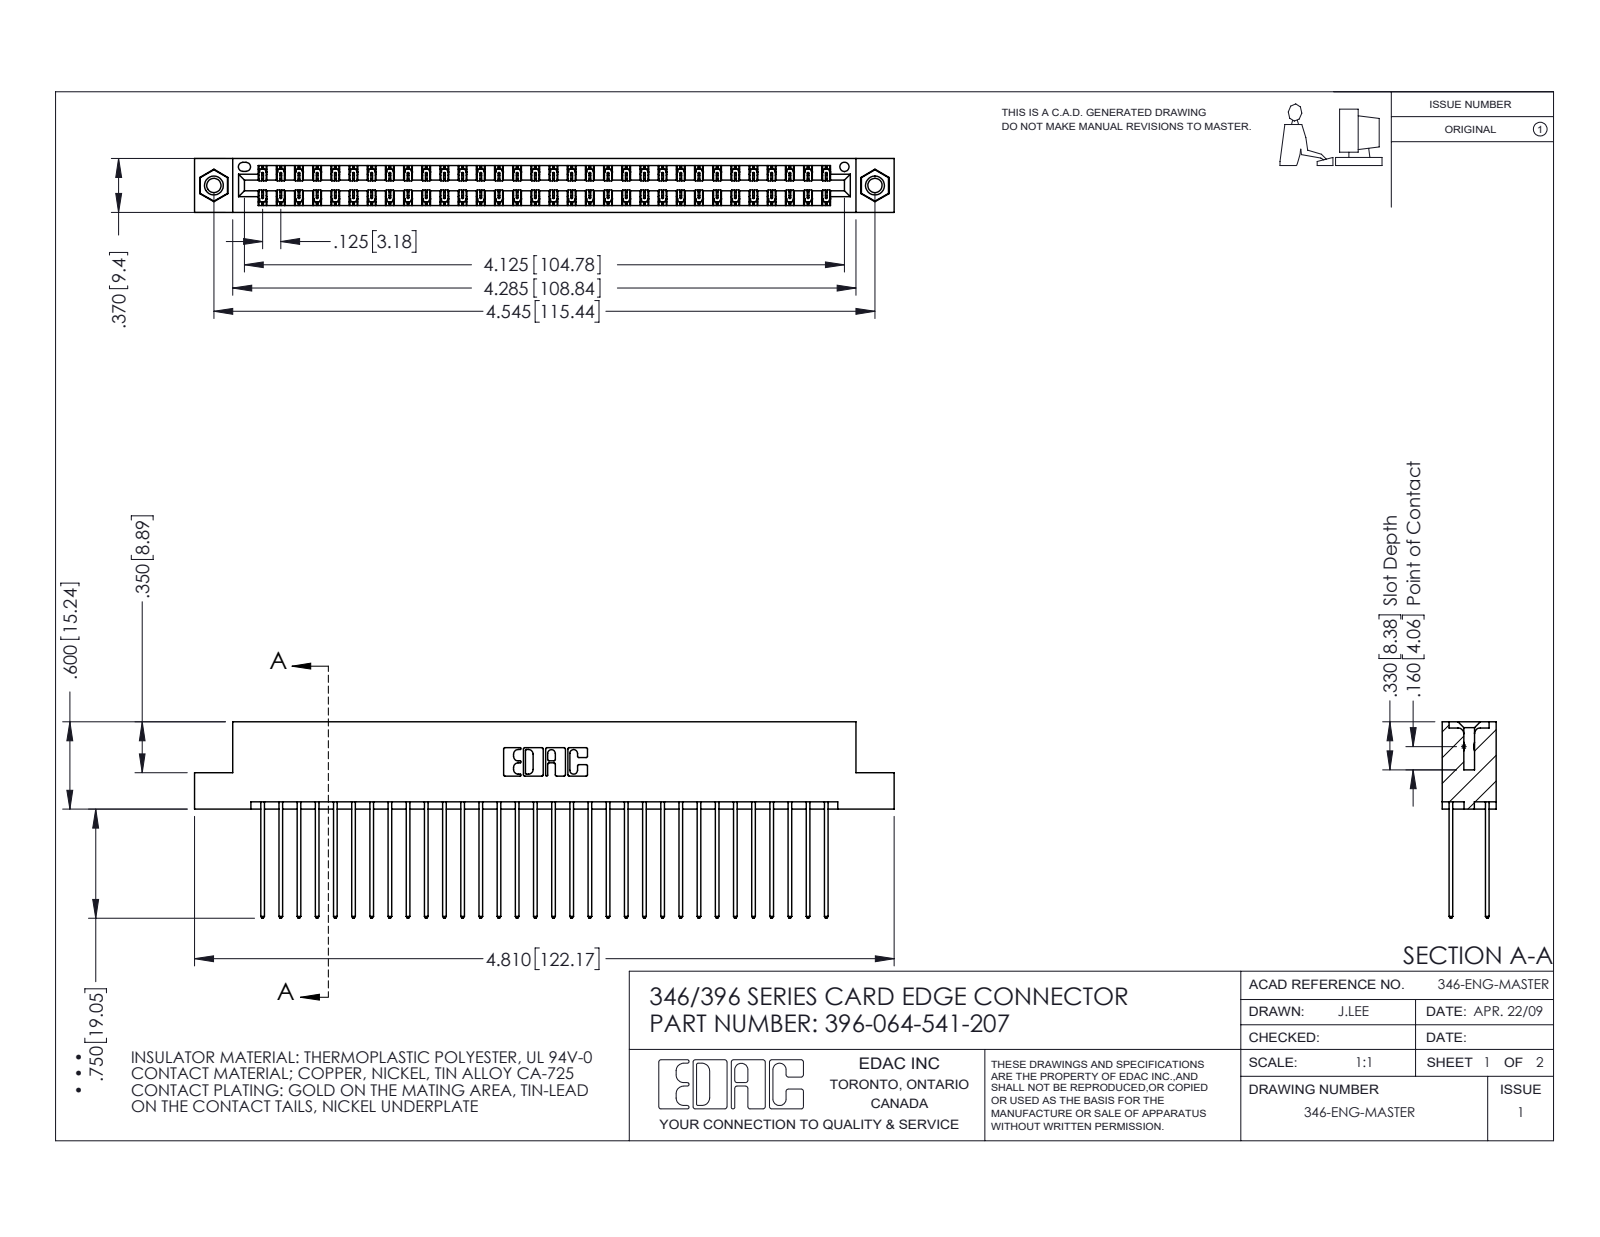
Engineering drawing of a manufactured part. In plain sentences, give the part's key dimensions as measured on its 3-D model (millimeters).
The part is named "345-250-001_345-250-005-103; 396-064-541-207; 345-292-001_345-293-141; 346 Part_Flush Mounting Lugs - 0.156 Dia-TI". Its 3-D file was written by "SolidWorks 2016 (CONFIG_CONTROL_DESIGN)". It is 67 solids with 3510 faces: 2348 planar, 1146 cylindrical and 16 other. Overall it measures 122.2 by 34.3 by 9.4 millimeters. Its volume is 12 200 cubic millimeters and its surface area 18 390 square millimeters. Round holes: 2 of diameter 2.5, 2 of diameter 3.2, 2 of diameter 4, 1 of diameter 1.6. Round bosses or shafts: 2 of diameter 3.9. Partial cylindrical surfaces (rounded edges, fillets, slot ends): 96 of radius 0.2, 64 of radius 0.3, 22 of radius 0.3, 6 of radius 0.2, 6 of radius 0.8, 3 of radius 0.7, 2 of radius 0.4, 2 of radius 0.6. The main face-to-face distances are 1.2, 8.2, 6.4, 1.8, 7.6, 0.6, 9.4, 7, 5.7, 3.8. The hole center spacings are 6.2, 110.2, 115.4.
